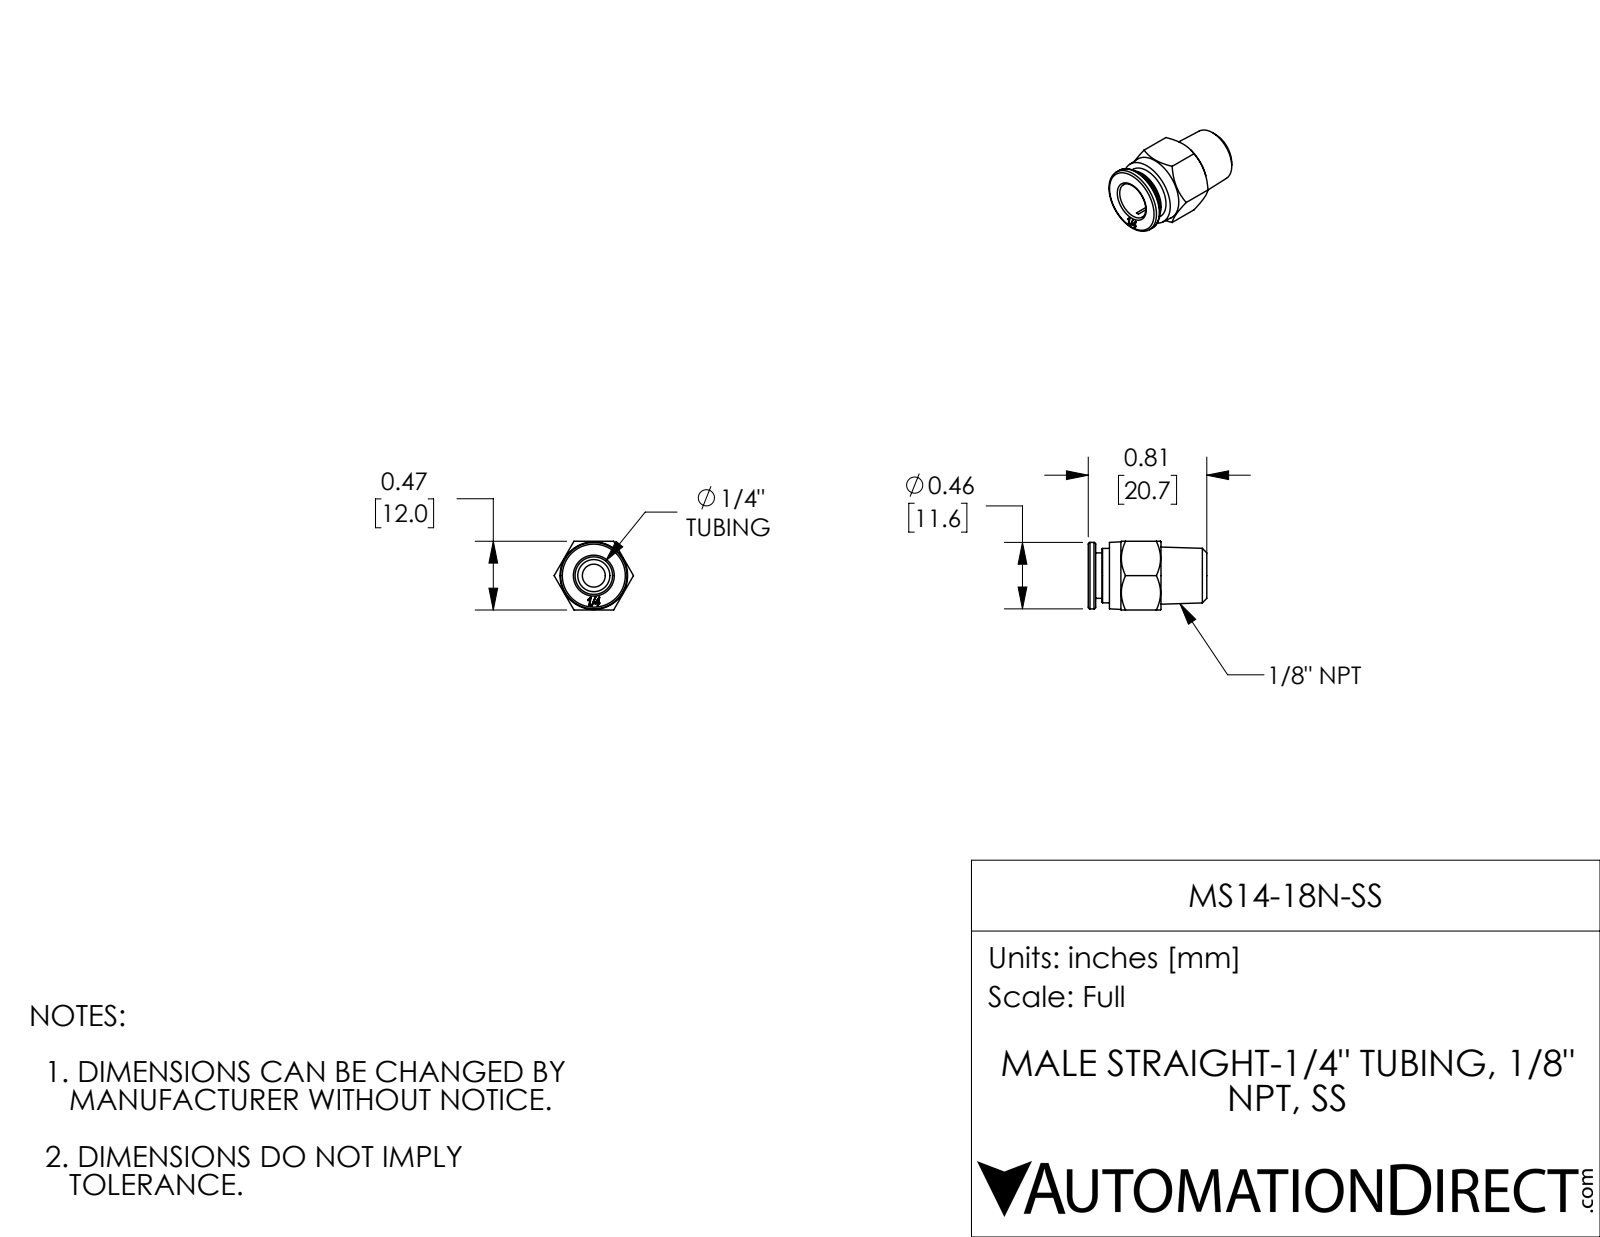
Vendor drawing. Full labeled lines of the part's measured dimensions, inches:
Part name (STEP PRODUCT): MS14-18N-SS
STEP written by: SolidWorks 2017 (AUTOMOTIVE_DESIGN)
Units: inches
Bodies: 1 solid, 87 faces (47 planar, 12 cylindrical, 28 other)
Overall size (bounding box): 0.815 × 0.546 × 0.472
Volume: 0.082 in³ · Surface area: 2.239 in²
Round holes (diameter × count): ⌀0.157 ×1, ⌀0.258 ×1, ⌀0.319 ×1
Round bosses / shafts (diameter × count): ⌀0.457 ×1, ⌀0.374 ×1, ⌀0.313 ×1
Main face-to-face distances: 0.472, 0.051, 0.094, 0.146, 0.354, 0.449, 0.5, 0.315, 0.669, 0.764
